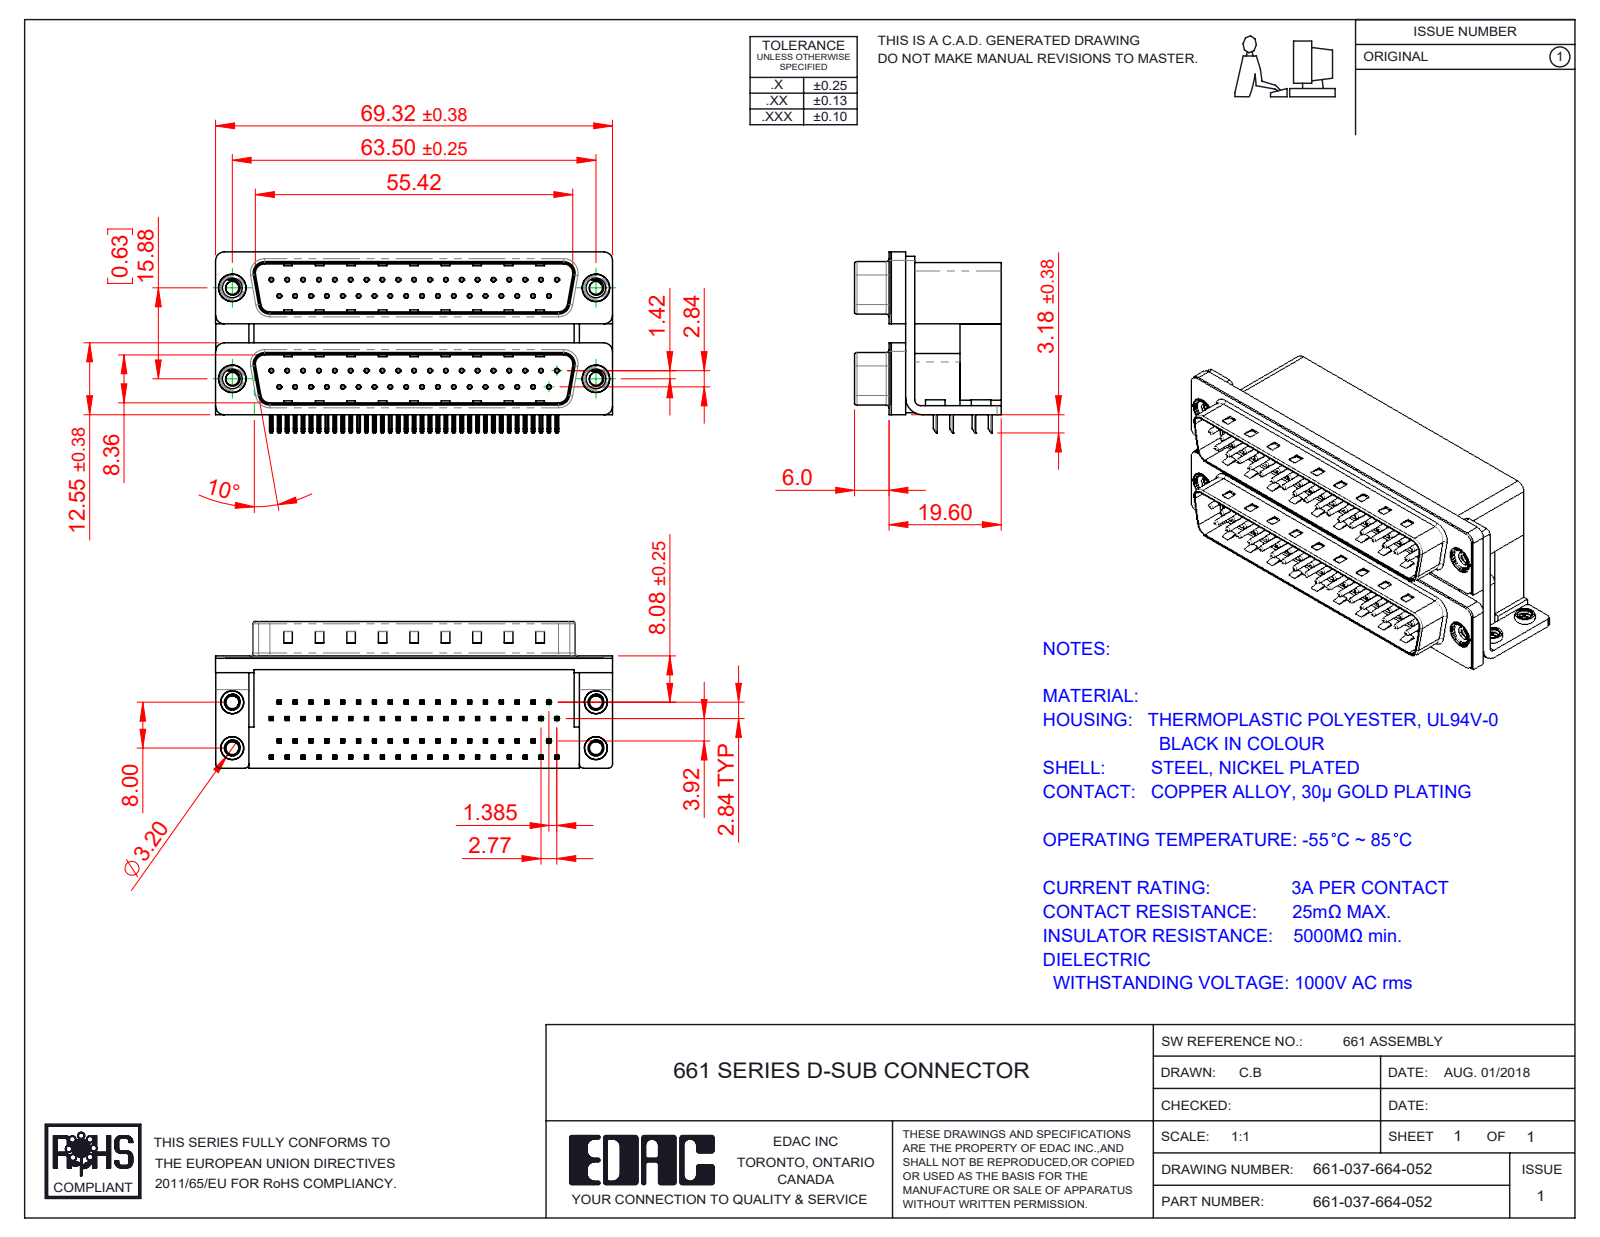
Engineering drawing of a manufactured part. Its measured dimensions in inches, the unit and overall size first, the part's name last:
Units: inches
Overall size (bounding box): 2.729 × 1.244 × 1.008
Round holes (diameter × count): ⌀0.014 ×74, ⌀0.031 ×74, ⌀0.089 ×8, ⌀0.108 ×4, ⌀0.126 ×4, ⌀0.138 ×4, ⌀0.157 ×4, ⌀0.189 ×4, ⌀0.197 ×4
Round bosses / shafts (diameter × count): ⌀0.03 ×74, ⌀0.193 ×4, ⌀0.187 ×4, ⌀0.157 ×4, ⌀0.154 ×4, ⌀0.134 ×4
Partial cylindrical surfaces — rounded edges, fillets, slot ends (radius × count): R0.01 ×296, R0.005 ×148, R0.02 ×16, R0.059 ×13, R0.03 ×8, R0.035 ×8, R0.063 ×8, R0.079 ×8
Main face-to-face distances: 0.016, 0.756, 0.625, 0.283, 0.472, 0.421, 0.345, 0.611, 1.032, 0.086
Hole centre spacings: 0.109, 0.218, 0.124, 0.327, 0.436, 0.545, 0.654, 0.763
Volume: 1.707 in³ · Surface area: 44.66 in²
Bodies: 89 solids, 6722 faces (4262 planar, 1870 cylindrical, 590 other)
Part name (STEP PRODUCT): 661 Housing Lower_37 Contacts; 661 4-40 Threaded Board Mount; 661 Threaded Rivet_4-40; 661 Housing Upper_37 Contacts L (+8 more)
STEP written by: SolidWorks 2020 (CONFIG_CONTROL_DESIGN)
